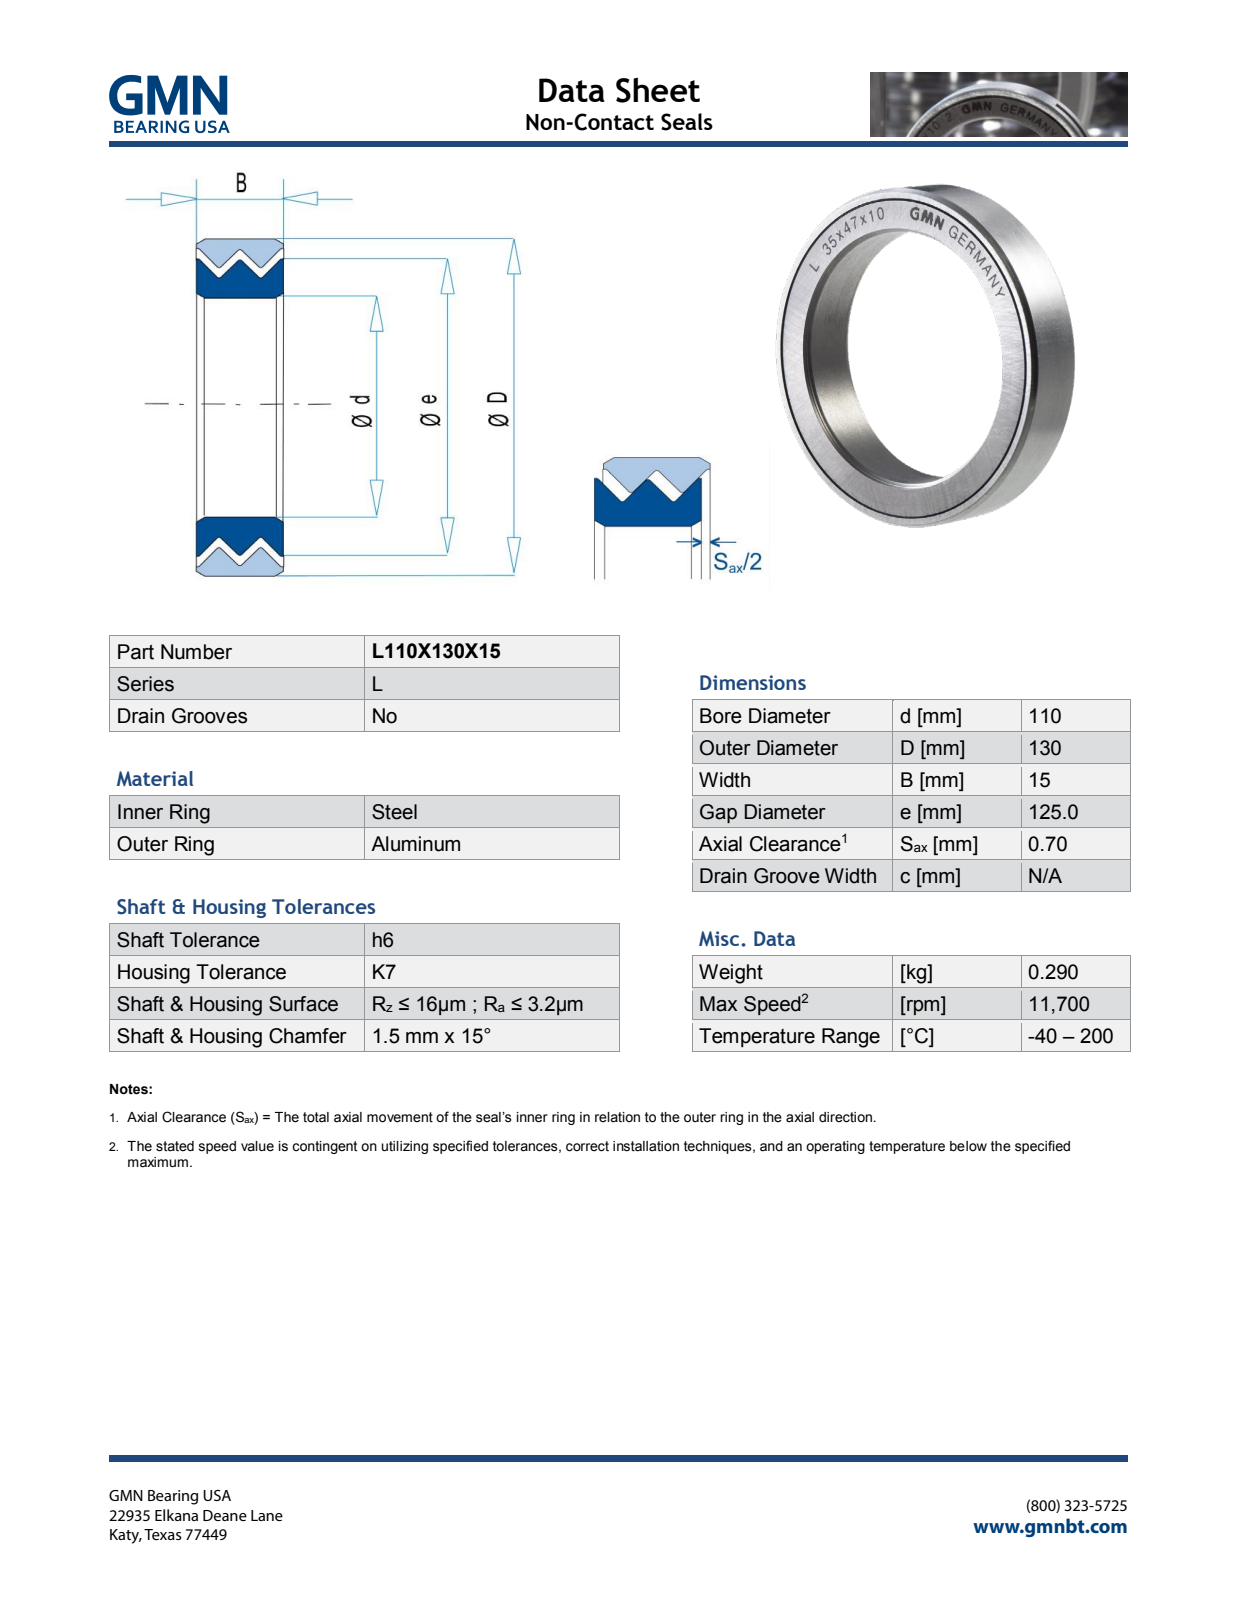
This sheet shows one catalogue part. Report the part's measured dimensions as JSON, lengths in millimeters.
{"part_name": "L110X130X15_PRT", "step_written_by": "PRO/ENGINEER BY PARAMETRIC TECHNOLOGY CORPORATION, 2013150 (AUTOMOTIVE_DESIGN)", "units": "millimeters", "bodies": {"solids": 2, "faces": 590, "planar": 534, "cylindrical": 12, "other": 44}, "overall_size": [130, 130, 15.07], "volume_mm3": 53115, "surface_area_mm2": 31164, "round_holes": [[110, 1], [125.49, 1]], "round_bosses_or_shafts": [[130, 1], [125, 1]], "face_to_face_distances": [15, 15.07, 0.54, 0.55, 4.34, 4.35, 3.8, 3.08, 0.46, 3.26]}
